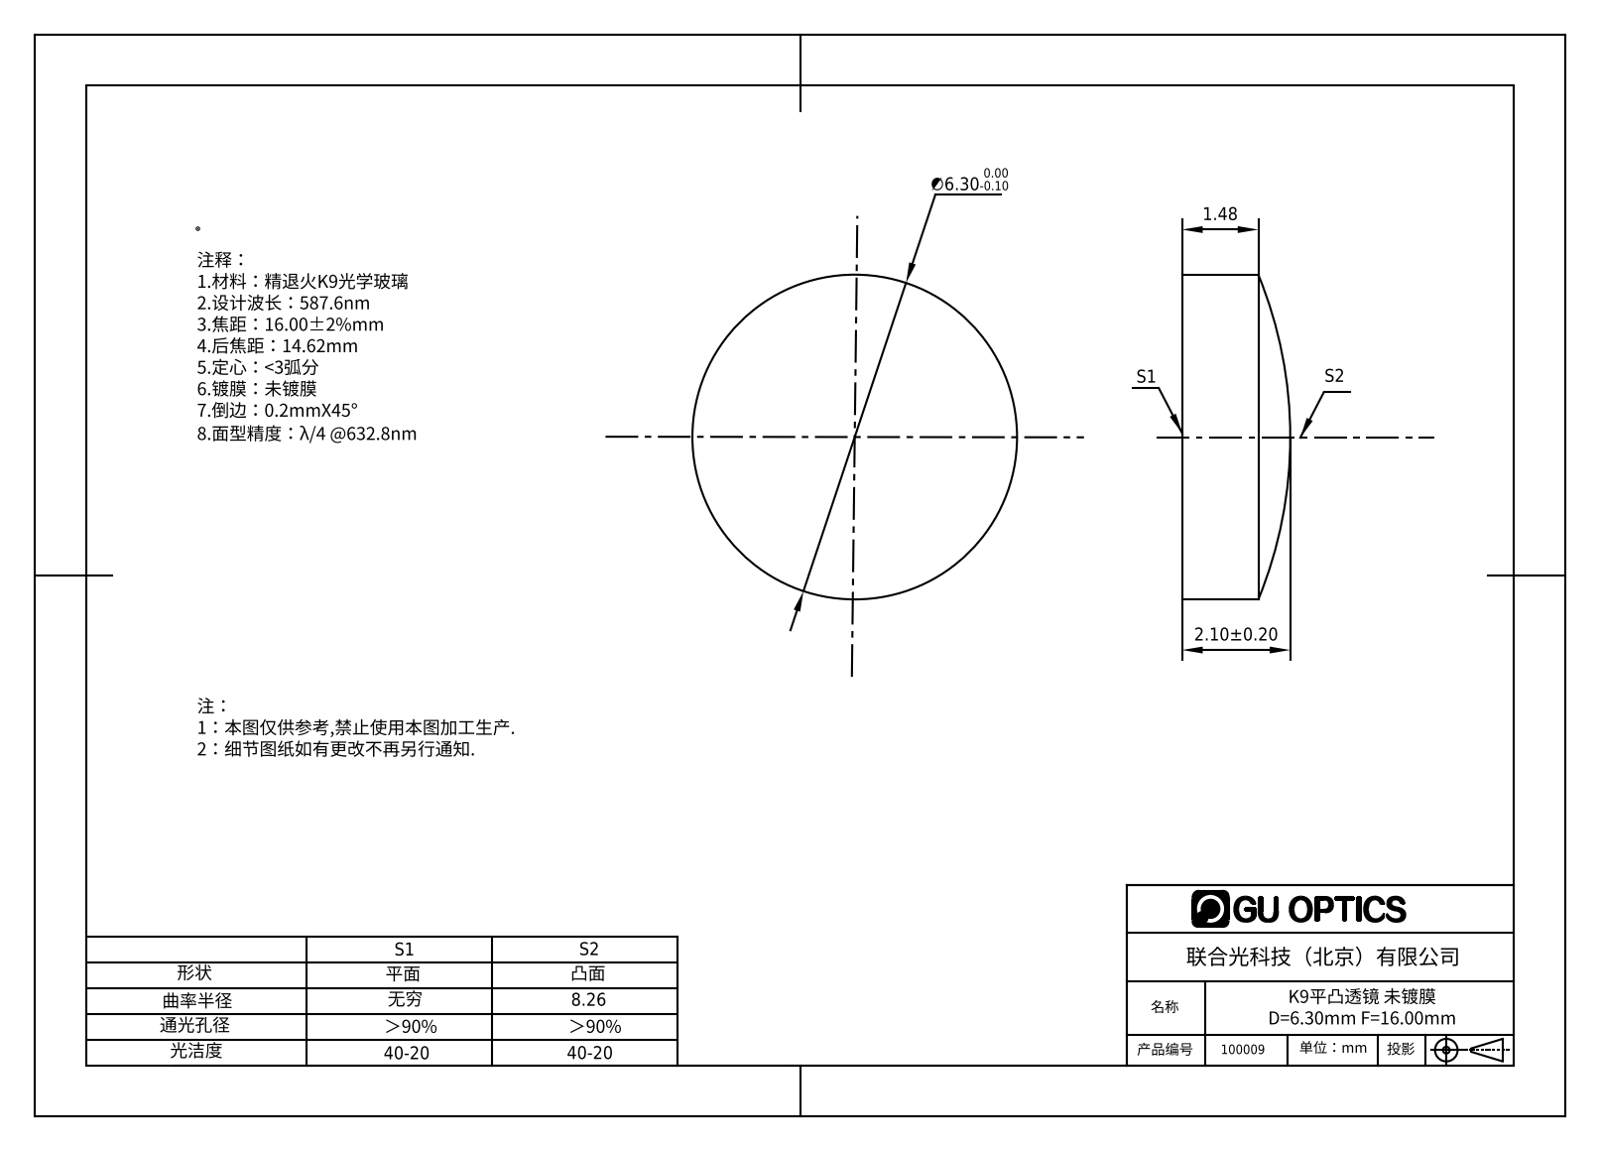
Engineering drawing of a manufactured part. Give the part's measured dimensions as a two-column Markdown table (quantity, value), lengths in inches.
| quantity | value |
| --- | --- |
| part name | 100009 |
| STEP written by | SolidWorks 2016 (AUTOMOTIVE_DESIGN) |
| units | inches |
| bodies | 1 solid, 5 faces (1 planar, 2 cylindrical, 2 other) |
| overall size | 0.248 × 0.248 × 0.083 |
| volume | 0.003 in³ |
| surface area | 0.14 in² |
| round bosses / shafts (diameter × count) | 0.248 × 1 |
